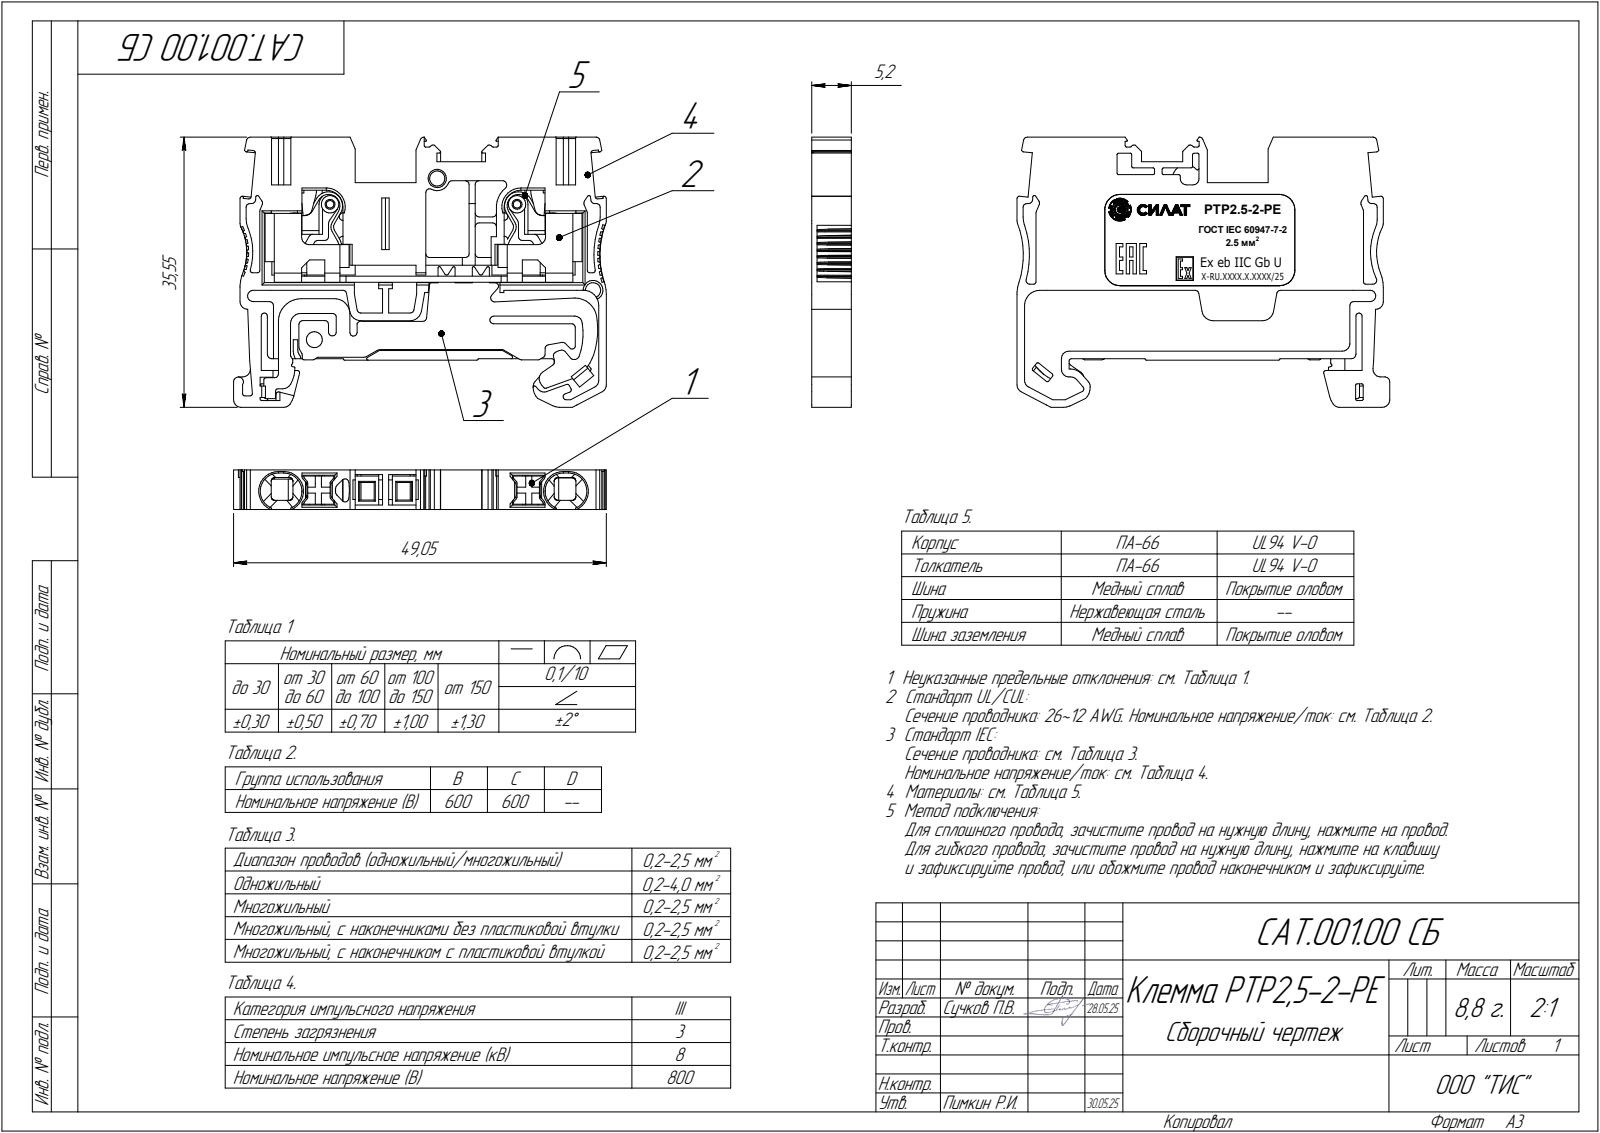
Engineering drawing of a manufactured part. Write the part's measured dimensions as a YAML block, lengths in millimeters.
part_name: "Клемма PTP2,5-2-PE"
step_written_by: "SolidWorks 2024 (AUTOMOTIVE_DESIGN)"
units: millimeters
bodies: {solids: 1, faces: 436, planar: 287, cylindrical: 144, other: 5}
overall_size: [49.05, 35.55, 5.2]
volume: 6810
surface_area: 4282
partial_cylinders:
  - {radius: 0.15, count: 36}
  - {radius: 0.3, count: 26}
  - {radius: 0.5, count: 24}
  - {radius: 0.2, count: 7}
  - {radius: 1, count: 7}
  - {radius: 2.4, count: 4}
  - {radius: 5, count: 3}
  - {radius: 0.1, count: 2}
face_to_face_distances: [5.2, 0.6, 29.35, 29.15, 4.6, 3.6, 3.9, 6.4, 0.8, 6.2]
